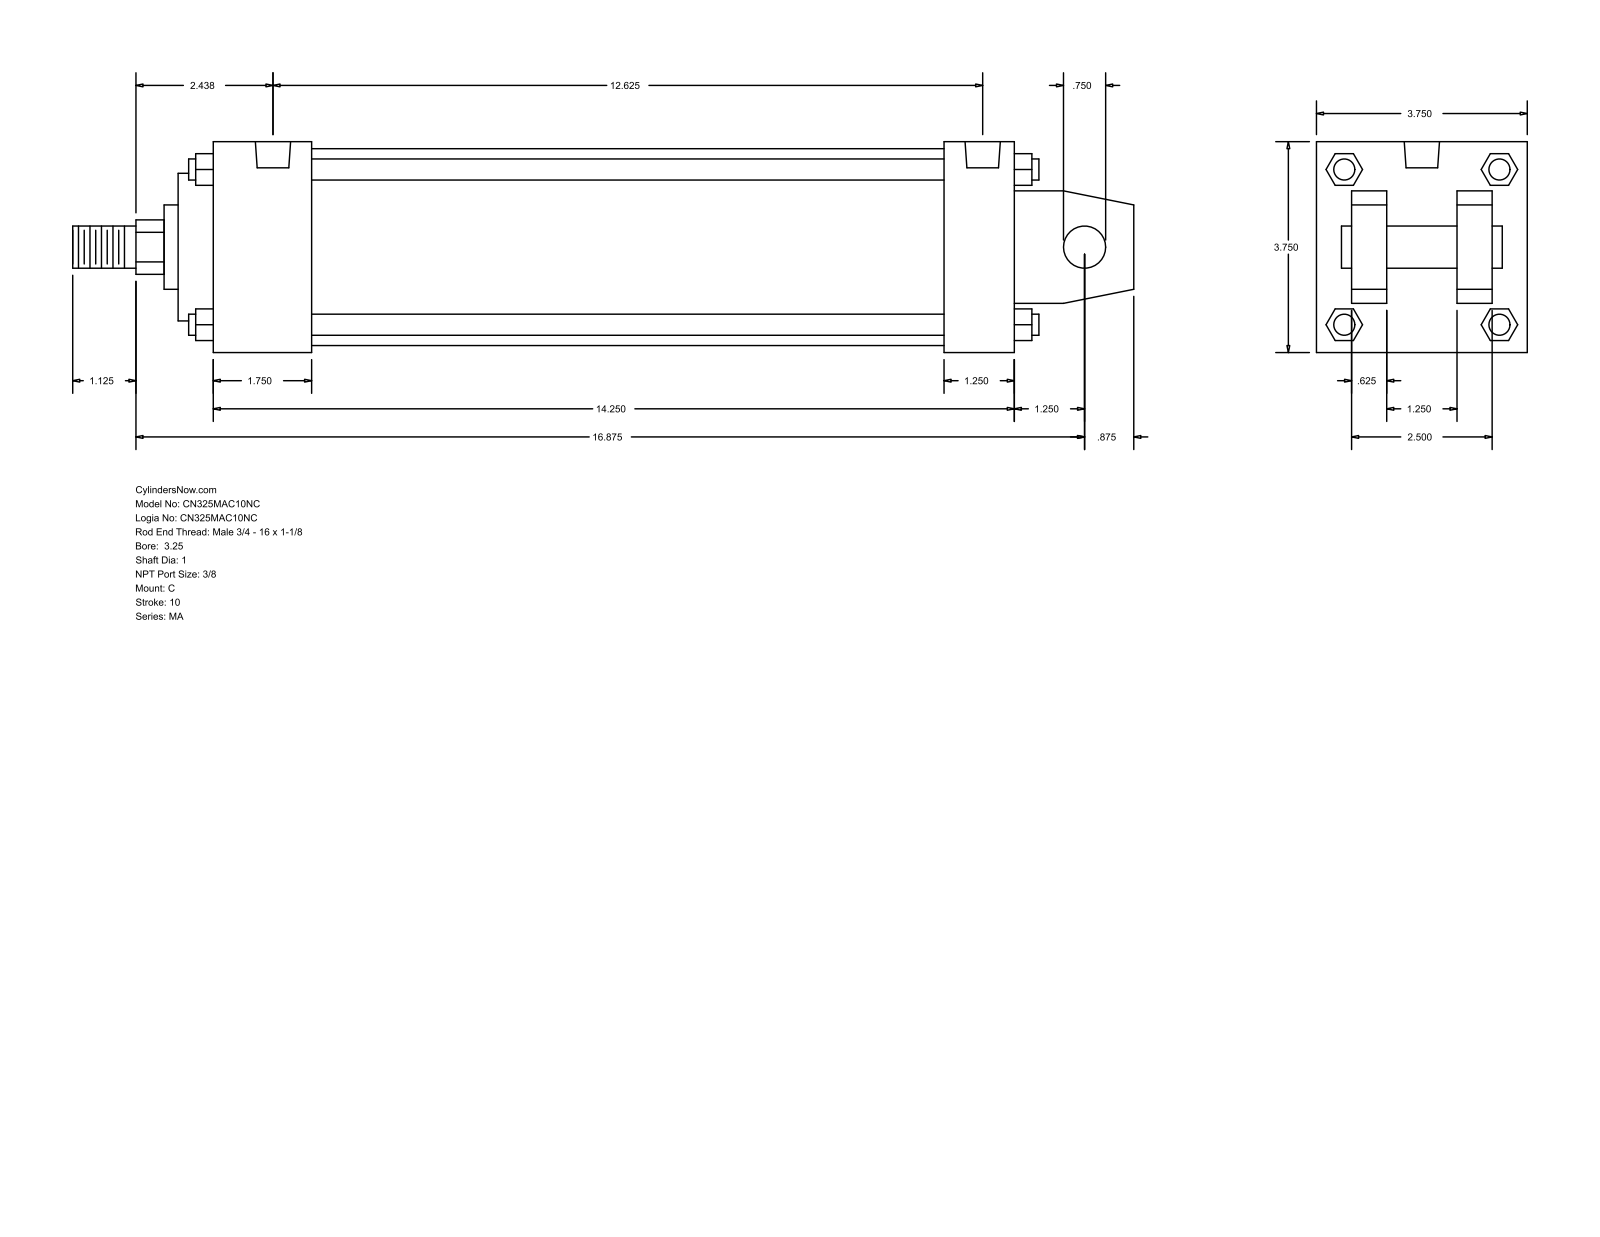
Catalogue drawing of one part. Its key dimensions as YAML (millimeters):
part_name: "MA_C__0325_1"
step_written_by: "GSSL Pune (CONFIG_CONTROL_DESIGN)"
units: millimeters
bodies: {solids: 0, faces: 141, planar: 109, cylindrical: 32, other: 0}
overall_size: [479.43, 95.25, 95.25]
round_holes:
  - {diameter: 11.11, count: 4}
  - {diameter: 15.93, count: 2}
round_bosses_or_shafts:
  - {diameter: 9.53, count: 4}
  - {diameter: 19.05, count: 2}
  - {diameter: 88.9, count: 1}
  - {diameter: 66.67, count: 1}
  - {diameter: 38.1, count: 1}
  - {diameter: 25.4, count: 1}
partial_cylinders:
  - {radius: 12.29, count: 1}
face_to_face_distances: [95.24, 15.87, 63.5, 361.96, 31.76, 31.74, 79.37, 47.63, 330.2, 44.46]
hole_center_spacings: [311.15, 4.76, 4.77, 315.91, 315.92, 320.68]
